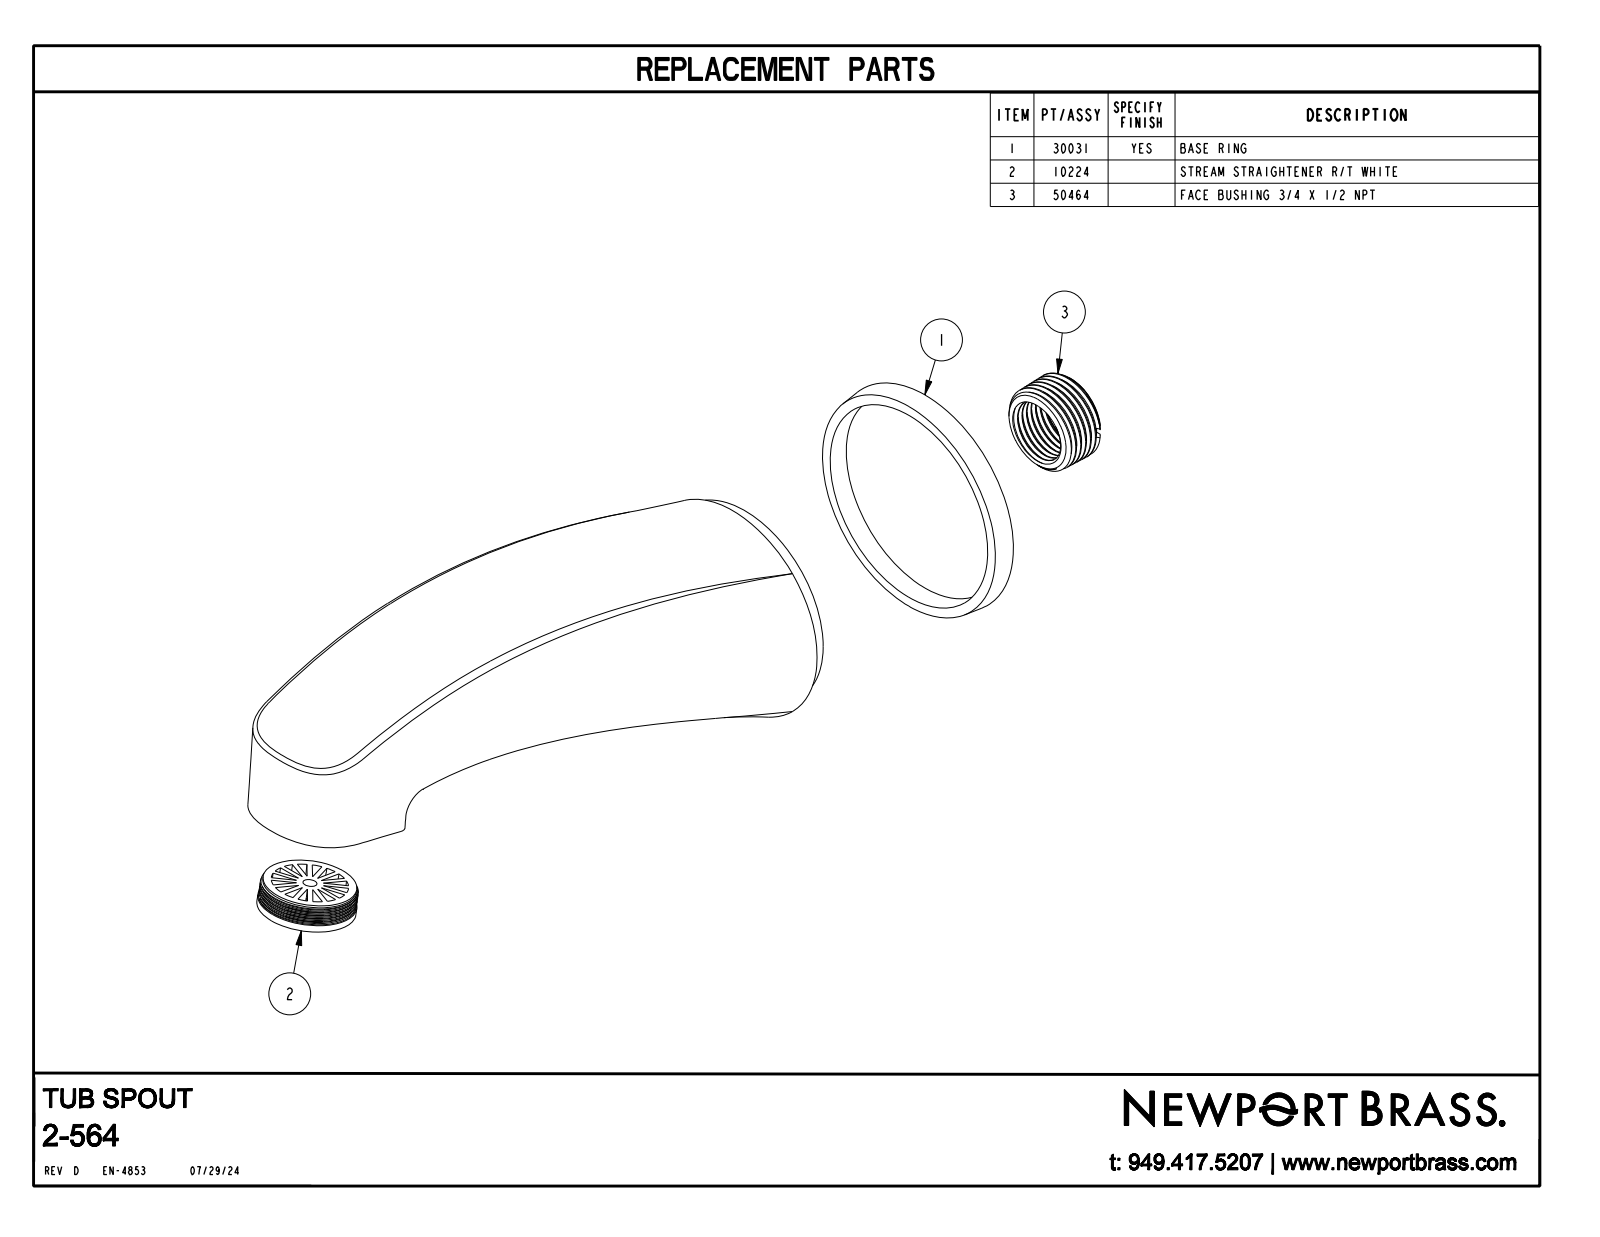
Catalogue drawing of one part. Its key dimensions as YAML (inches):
part_name: "30032; 30031; 2-564_ASM"
step_written_by: "CREO PARAMETRIC BY PTC INC, 2018400 (AUTOMOTIVE_DESIGN)"
units: inches
bodies: {solids: 2, faces: 20, planar: 6, cylindrical: 2, other: 12}
overall_size: [7.429, 3.323, 2.75]
volume: 23.7
surface_area: 69.03
round_bosses_or_shafts:
  - {diameter: 2.438, count: 1}
face_to_face_distances: [0.25, 0.062, 0.188]
